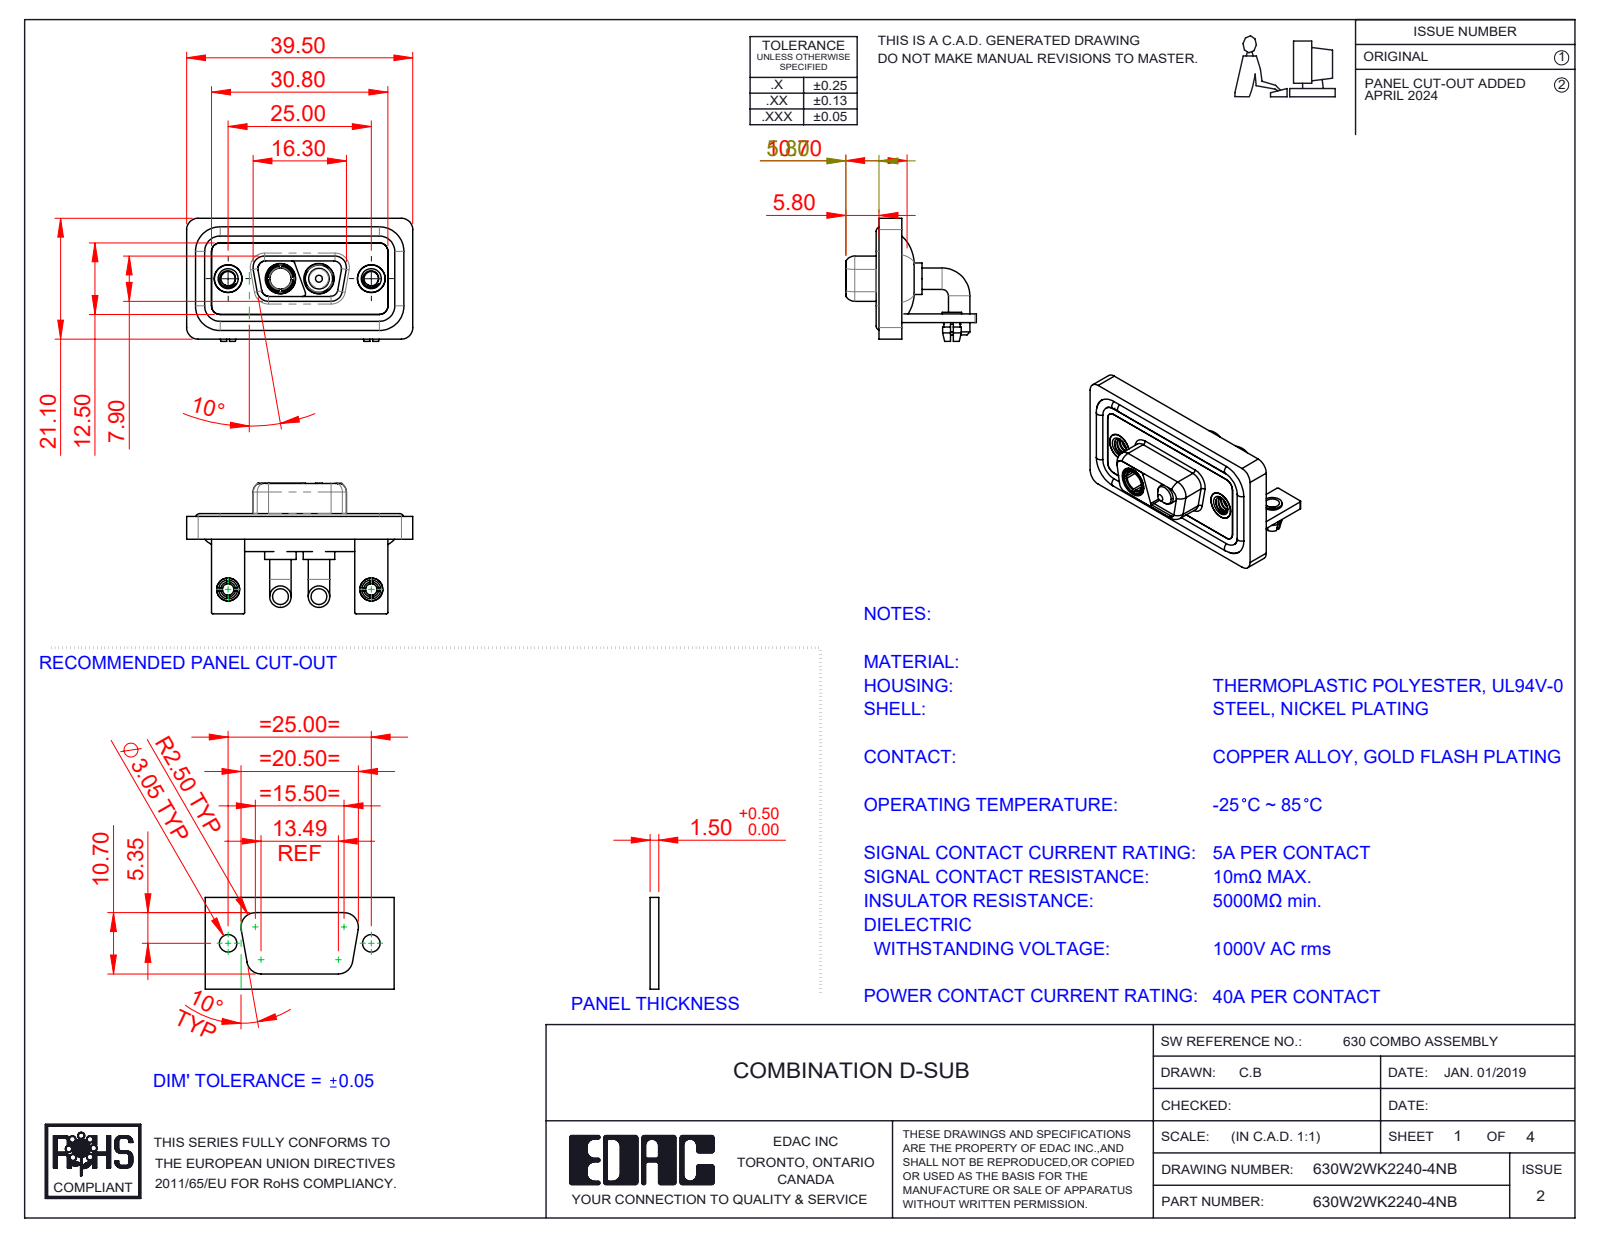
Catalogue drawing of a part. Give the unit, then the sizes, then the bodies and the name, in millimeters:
Units: millimetres
Overall size (bounding box): 39.5 × 22.8 × 21.5
Round holes (diameter × count): ⌀2.5 ×4, ⌀4.85 ×4, ⌀2 ×2, ⌀3.2 ×2, ⌀4 ×2, ⌀4.05 ×2, ⌀5 ×2, ⌀5.3 ×2, ⌀3.7 ×1
Round bosses / shafts (diameter × count): ⌀3.75 ×4, ⌀1.6 ×4, ⌀5.5 ×2, ⌀5.2 ×2, ⌀4.95 ×2, ⌀4.8 ×2, ⌀4.75 ×2, ⌀4 ×2
Partial cylindrical surfaces — rounded edges, fillets, slot ends (radius × count): R2 ×19, R1.5 ×18, R0.25 ×16, R1.35 ×8, R1.6 ×8, R0.5 ×7, R0.6 ×4, R0.65 ×4
Main face-to-face distances: 0.4, 2.9, 1.5, 1.1, 3.7, 1.8, 0.8, 2.5, 1.6, 3.1
Hole centre spacings: 9.14, 15.86, 25, 6.72
Volume: 5 248 mm³ · Surface area: 8 531 mm²
Bodies: 15 solids, 642 faces (212 planar, 289 cylindrical, 141 other)
Part name (STEP PRODUCT): Power Socket_40A RA; 630Combo Threaded Rivet_A; Power Pin_40A RA; 630Combo Board Lock_50 Contacts (+6 more)
STEP written by: SolidWorks 2023 (CONFIG_CONTROL_DESIGN)
